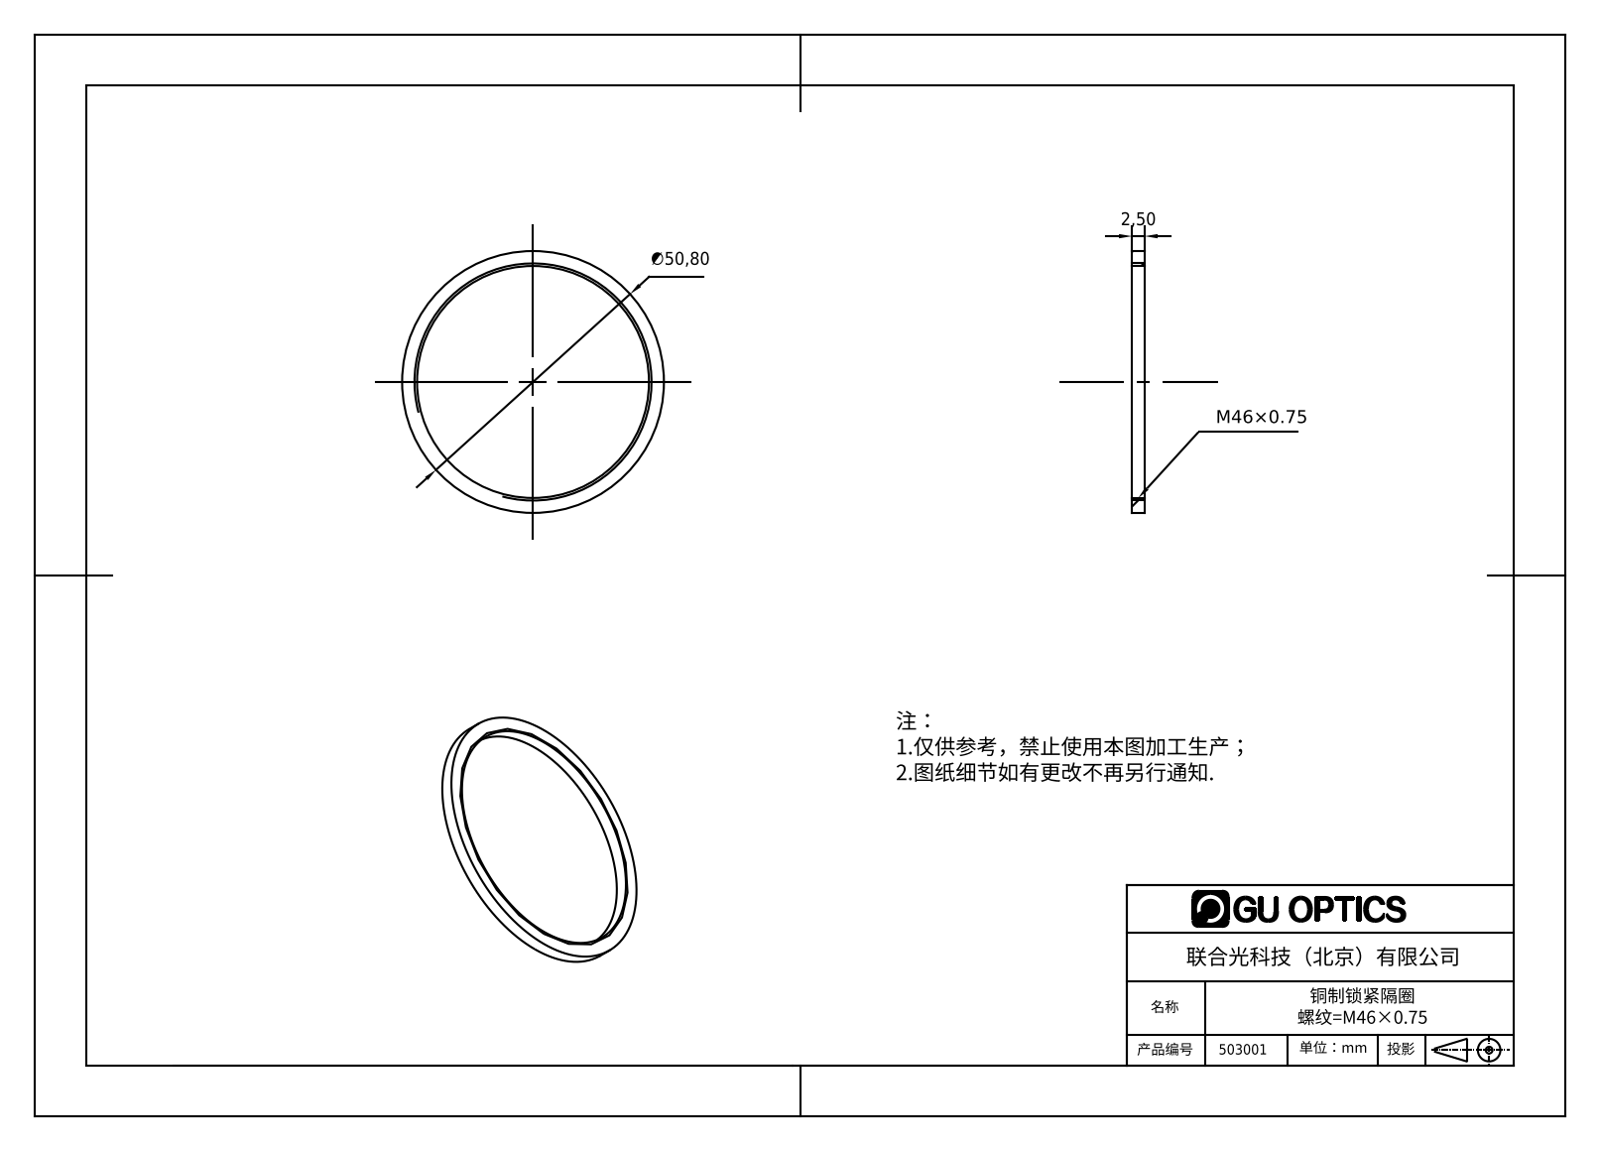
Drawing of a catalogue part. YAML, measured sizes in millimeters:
part_name: "511001"
step_written_by: "SolidWorks 2016 (AUTOMOTIVE_DESIGN)"
units: millimeters
bodies: {solids: 1, faces: 6, planar: 2, cylindrical: 4, other: 0}
overall_size: [50.8, 50.8, 2.5]
volume: 1091
surface_area: 1625
round_holes:
  - {diameter: 45, count: 1}
round_bosses_or_shafts:
  - {diameter: 50.8, count: 1}
face_to_face_distances: [2.5]
